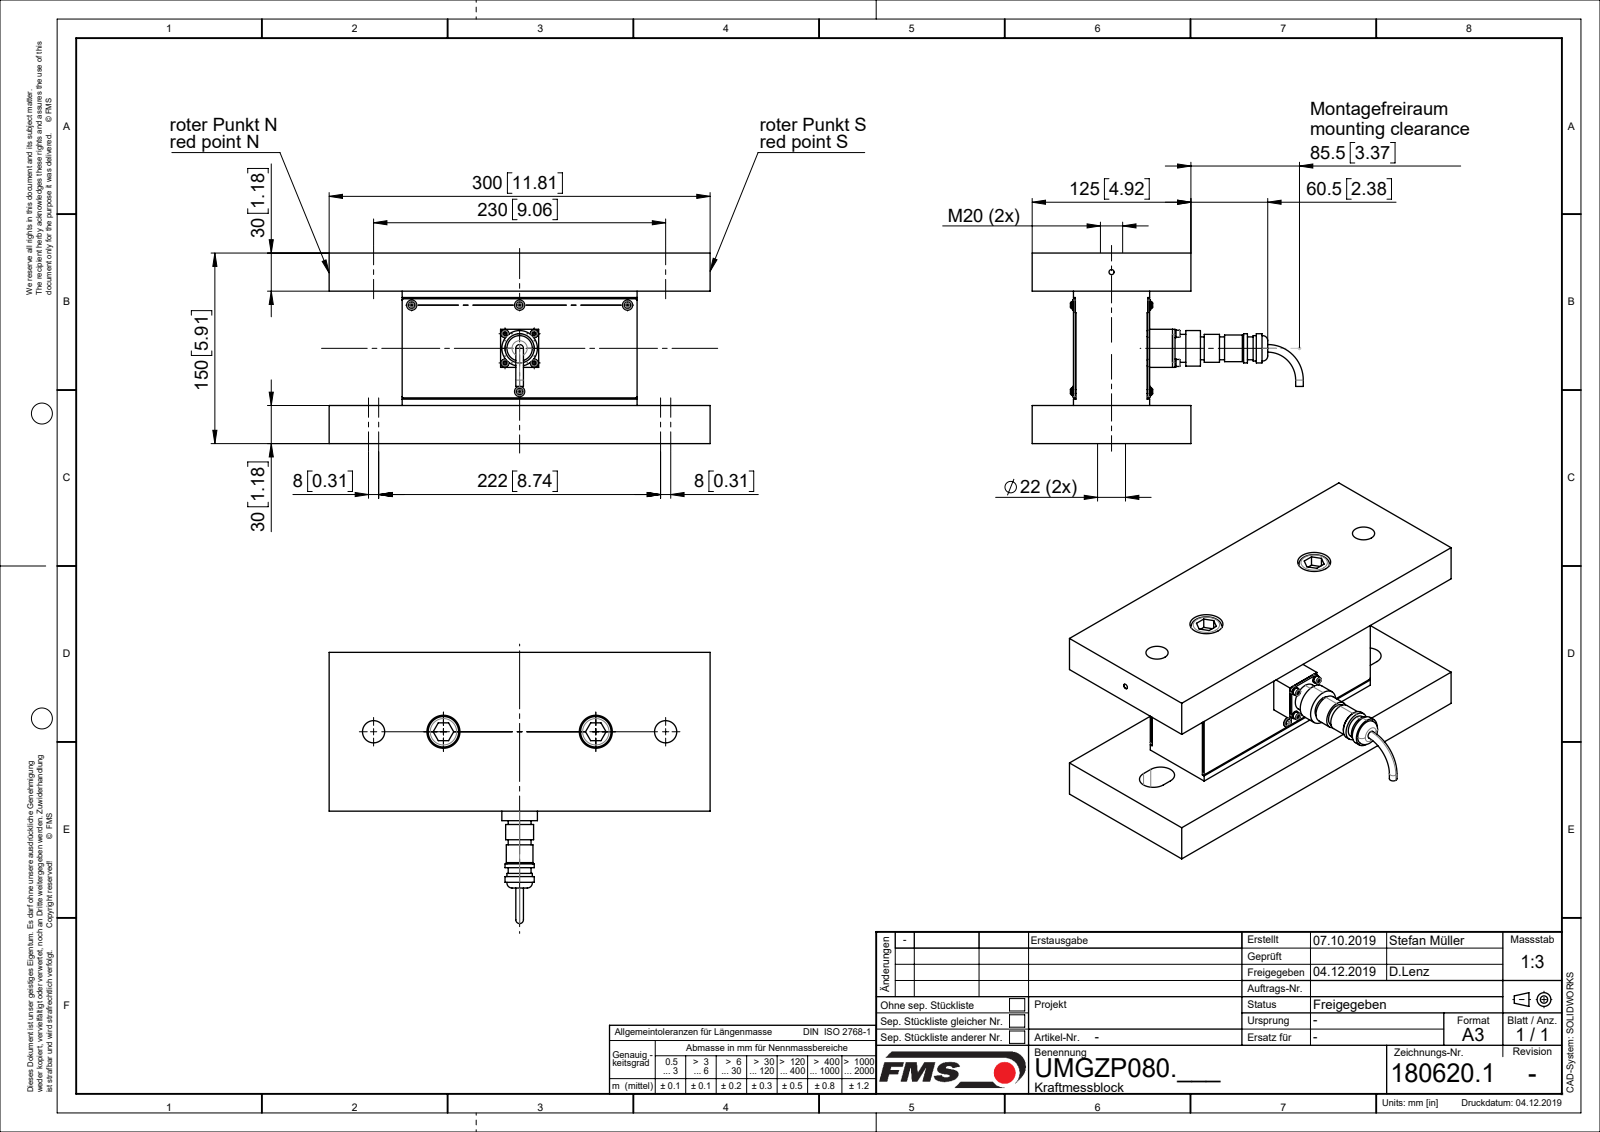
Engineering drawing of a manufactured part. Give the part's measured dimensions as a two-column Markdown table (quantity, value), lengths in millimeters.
| quantity | value |
| --- | --- |
| part name | U1806201_STP; U5142704; U51438; U51431 (+8 more) |
| STEP written by | Mechanical Desktop 2009 (CONFIG_CONTROL_DESIGN) |
| units | millimeters |
| bodies | 36 solids, 668 faces (274 planar, 268 cylindrical, 126 other) |
| overall size | 300 × 213.5 × 177 |
| volume | 3 095 000 mm³ |
| surface area | 408 441 mm² |
| round holes (diameter × count) | 2.5 × 4, 2.6 × 4, 3.2 × 4, 3.4 × 4, 4.25 × 4, 6 × 3, 23 × 3, 14.21 × 2, 18 × 2, 21 × 2, 26 × 2 |
| round bosses / shafts (diameter × count) | 3 × 8, 6.3 × 4, 6.2 × 4, 5.5 × 4, 2.5 × 4, 20 × 3, 37 × 2, 24 × 2 |
| partial cylindrical surfaces (radius × count) | 1 × 4, 4 × 4, 8 × 4, 11 × 4, 1.7 × 2, 6 × 2 |
| main face-to-face distances | 30, 120, 90, 150, 34, 91, 32.5, 92.5, 58.5, 1.5 |
| hole center spacings | 16.26, 23, 25.27, 46.93, 32.53, 34, 55, 76.87 |
